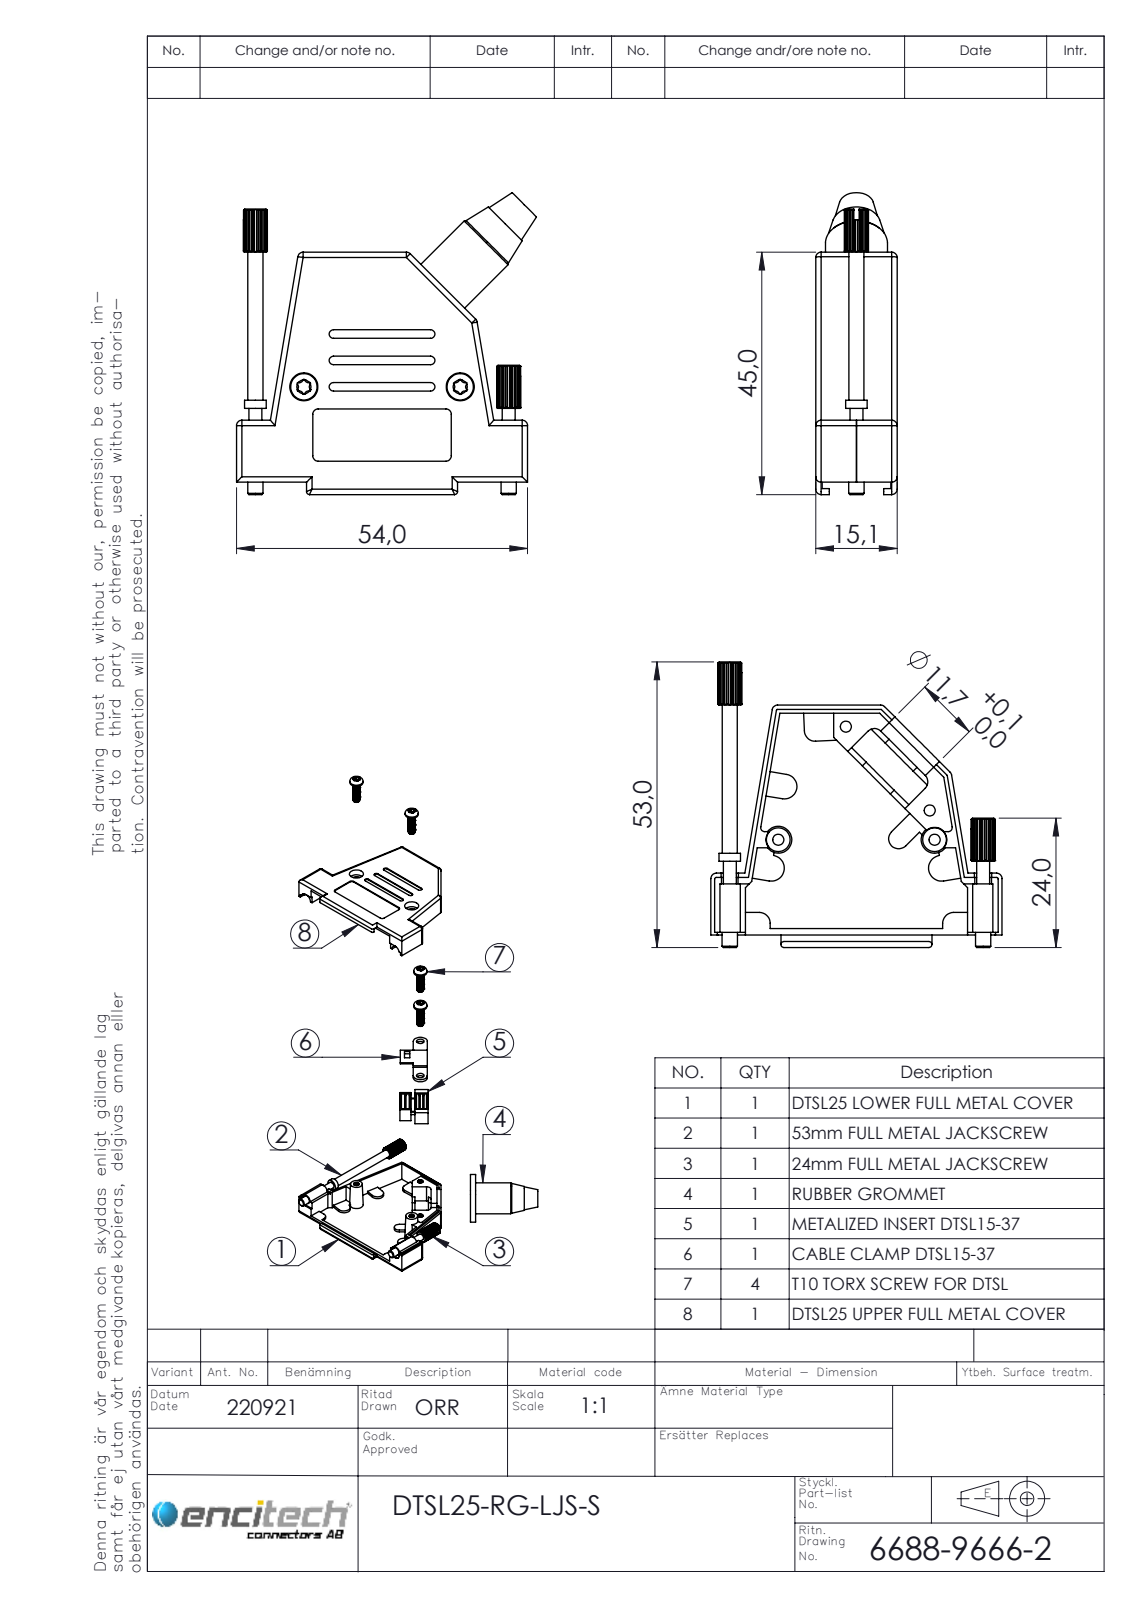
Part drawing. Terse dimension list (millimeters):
name: 6826-0147-01; 6805-0208-13; 6838-0111-32; 6830-0108-04 (+5 more)
written by: SolidWorks 2021 (AUTOMOTIVE_DESIGN)
unit: mm
bodies: 15 solids, 1133 faces (453 planar, 572 cylindrical, 108 other)
size: 56.05 × 55.66 × 15.1
volume: 10 545 mm³; area: 16 215 mm²
holes: 4× ⌀2.05, 4× ⌀2.8, 2× ⌀3.1, 2× ⌀3.2, 1× ⌀9
bosses: 4× ⌀4.9, 4× ⌀2.5, 2× ⌀7.1, 2× ⌀5.2, 2× ⌀2.84, 2× ⌀2.4, 1× ⌀11.5, 1× ⌀11.1
rounds: 37× R1, 24× R0.18, 24× R0.7, 10× R2, 6× R0.8, 4× R0.3, 4× R2.4, 2× R0.55
face distances: 1.2, 13.9, 12.7, 15.1, 1.5, 6.35, 13.6, 0.9, 7.55, 14.8
hole spacings: 5.52, 21.99, 24.45, 26.67, 28.61, 29, 47
